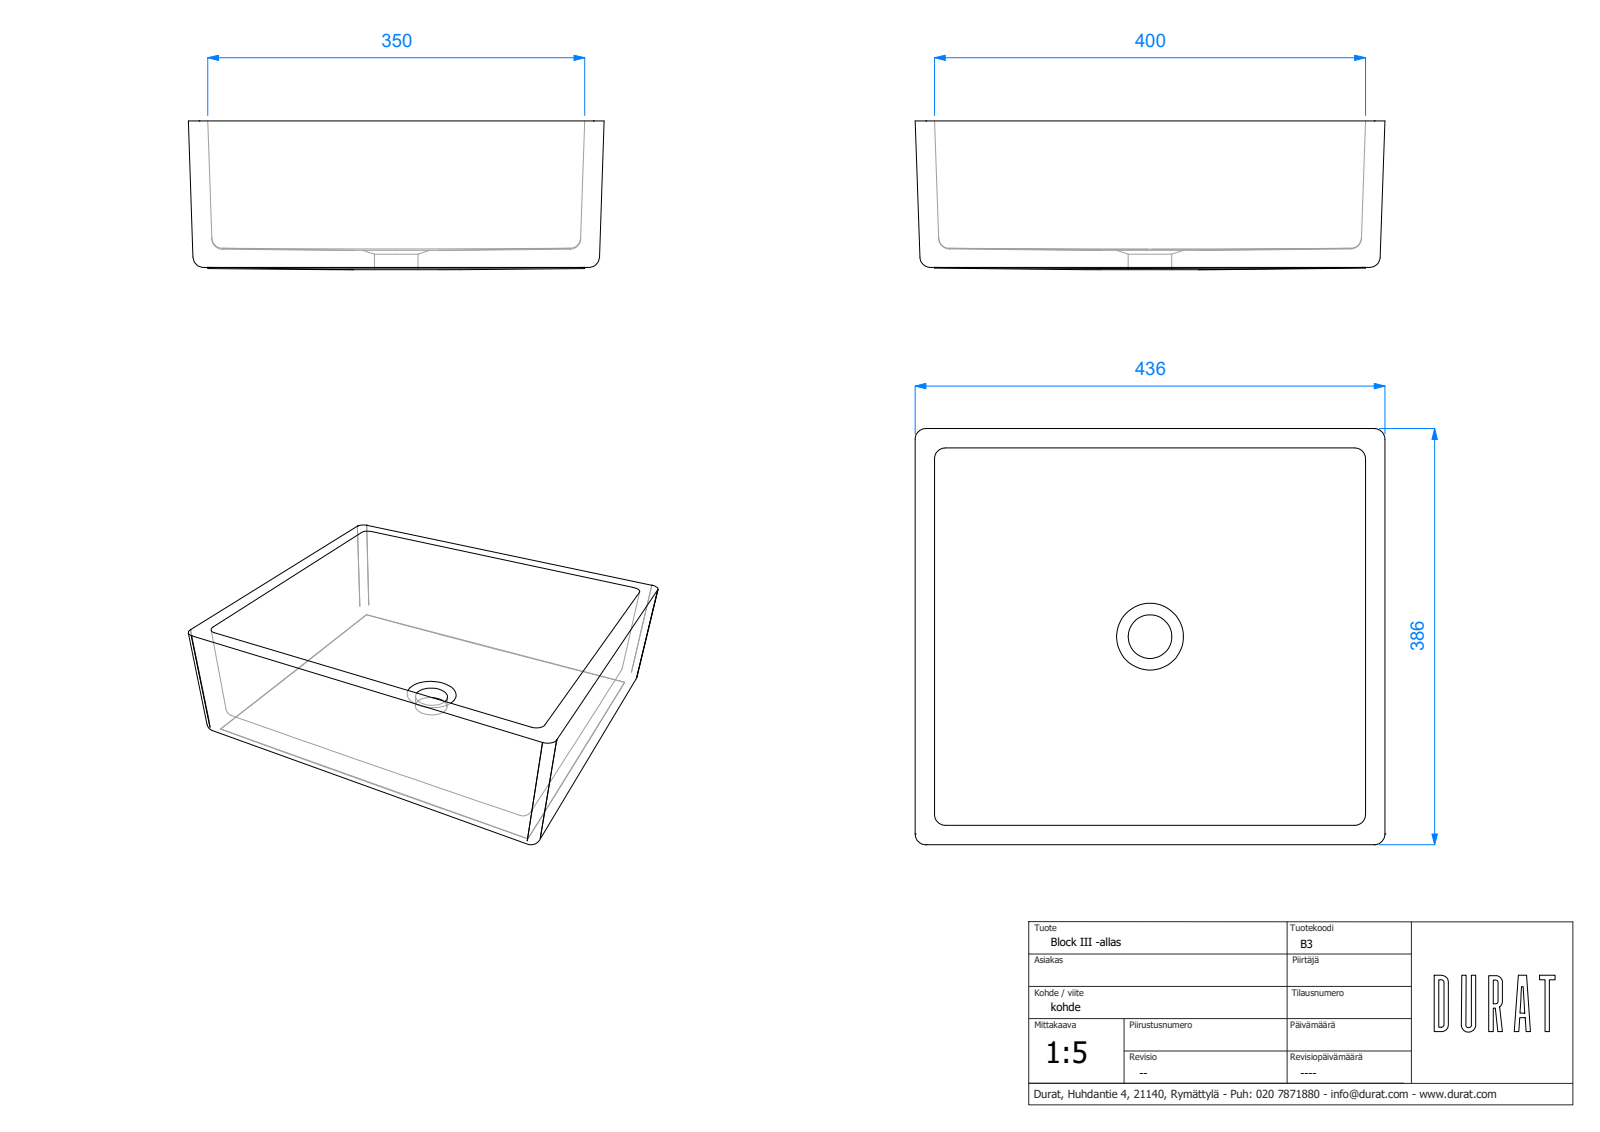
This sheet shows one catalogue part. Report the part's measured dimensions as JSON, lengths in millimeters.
{"step_written_by": "ST-DEVELOPER v15 (AUTOMOTIVE_DESIGN)", "units": "millimeters", "bodies": {"solids": 0, "faces": 48, "planar": 16, "cylindrical": 0, "other": 32}, "overall_size": [436.02, 386.02, 138.19], "face_to_face_distances": [18.01, 17.98, 17.97, 138.19, 18, 120.19, 2.19, 15.81, 136, 350]}
